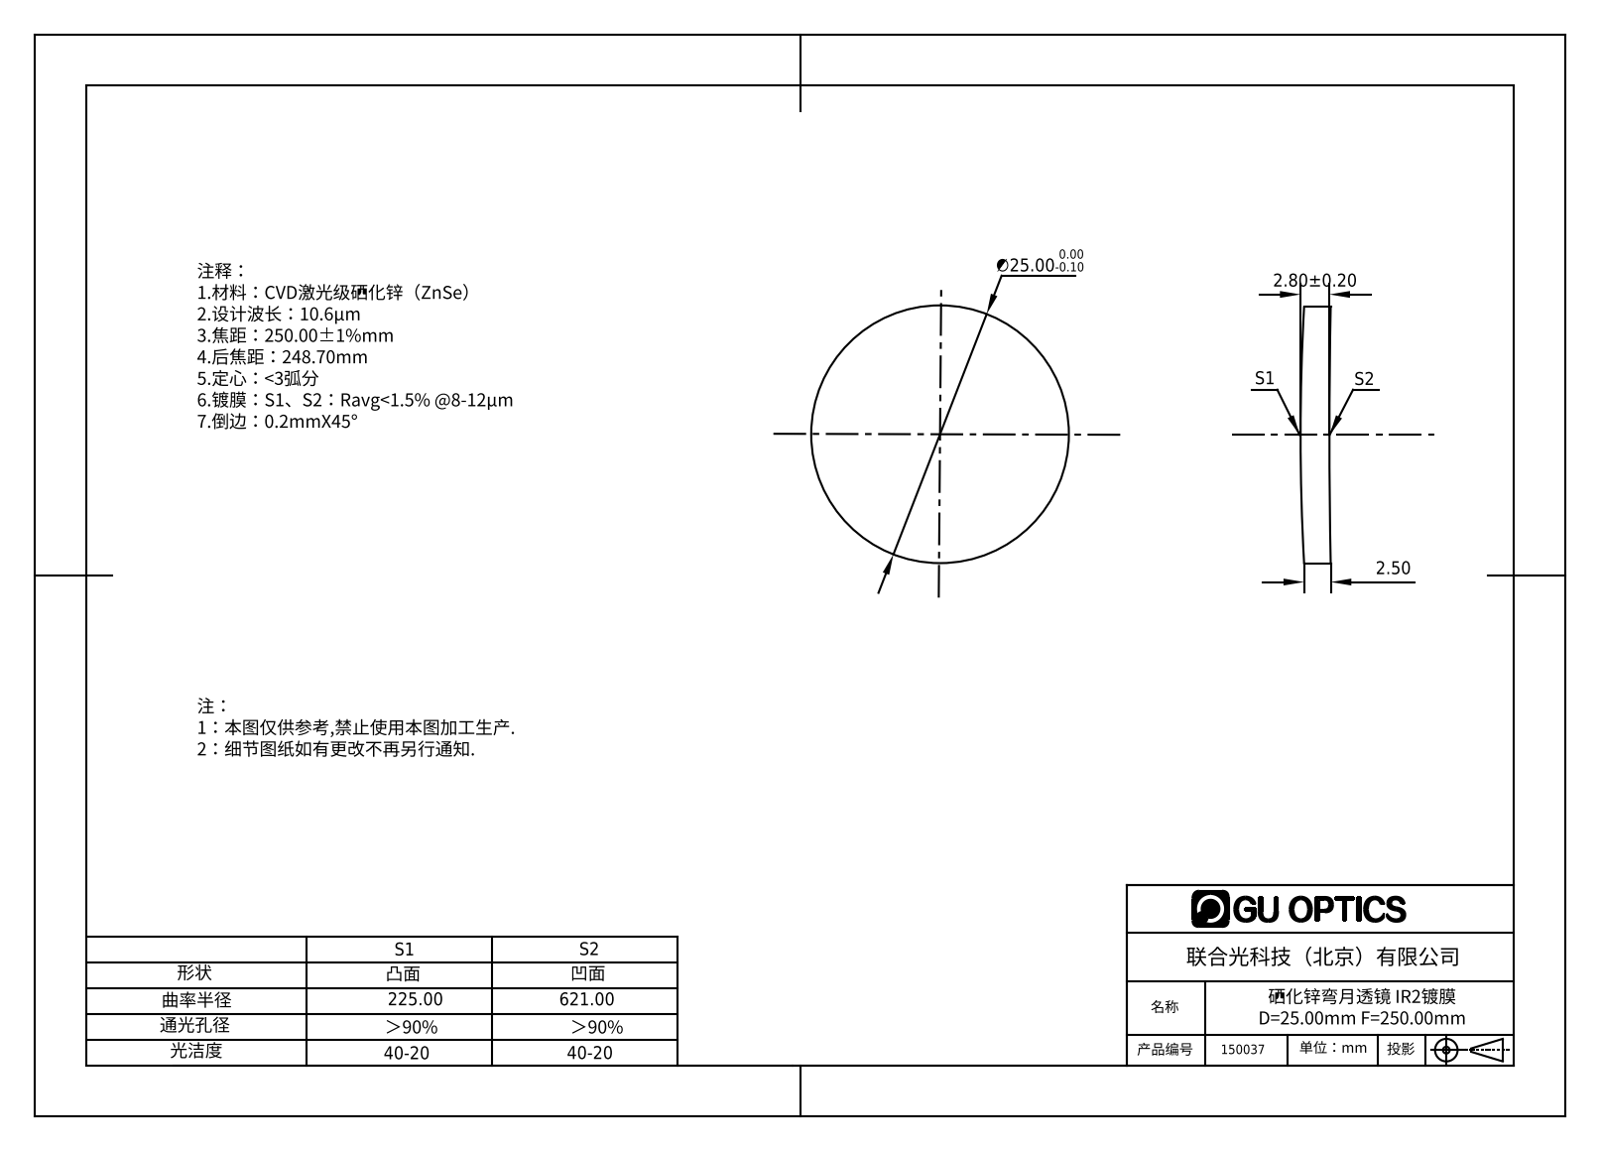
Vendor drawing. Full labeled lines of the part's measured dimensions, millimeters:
Part name (STEP PRODUCT): 150012
STEP written by: SolidWorks 2016 (AUTOMOTIVE_DESIGN)
Units: millimetres
Bodies: 1 solid, 6 faces (0 planar, 2 cylindrical, 4 other)
Overall size (bounding box): 25 × 25 × 2.93
Volume: 1 320 mm³ · Surface area: 1 185 mm²
Round bosses / shafts (diameter × count): ⌀25 ×1
